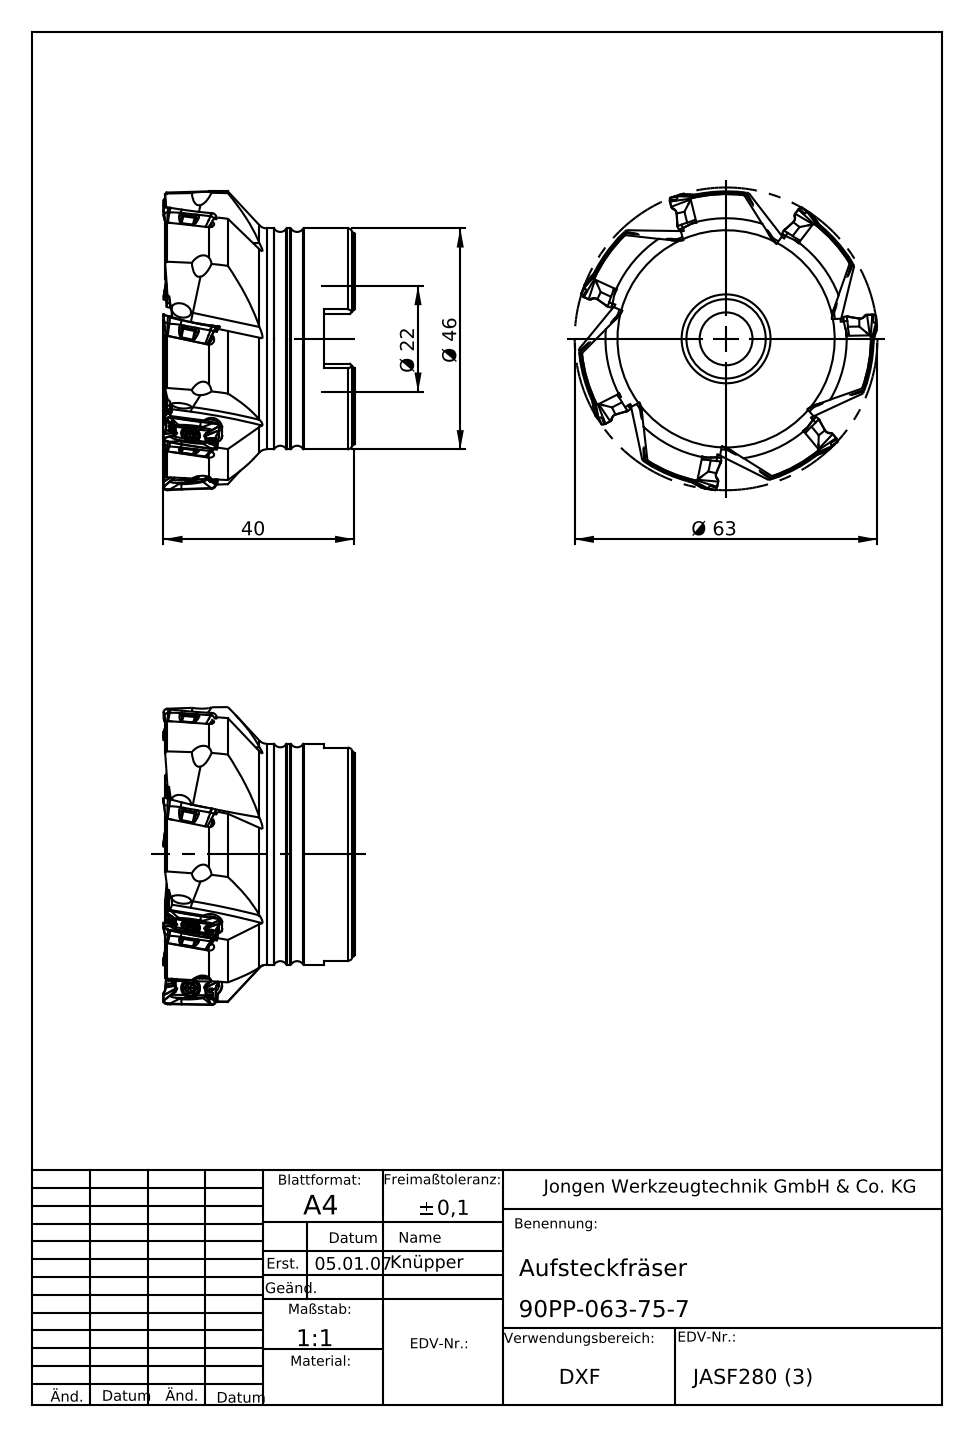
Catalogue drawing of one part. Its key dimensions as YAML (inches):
part_name: "90PP-063-75-7"
step_written_by: "SolidWorks 2012 (AUTOMOTIVE_DESIGN)"
units: inches
bodies: {solids: 1, faces: 296, planar: 102, cylindrical: 91, other: 103}
overall_size: [2.48, 2.48, 1.575]
volume: 4.104
surface_area: 27.48
round_holes:
  - {diameter: 0.118, count: 7}
  - {diameter: 0.433, count: 1}
  - {diameter: 0.65, count: 1}
  - {diameter: 0.866, count: 1}
  - {diameter: 0.872, count: 1}
  - {diameter: 0.878, count: 1}
  - {diameter: 2.074, count: 1}
round_bosses_or_shafts:
  - {diameter: 2.48, count: 1}
  - {diameter: 1.811, count: 1}
partial_cylinders:
  - {radius: 0.059, count: 14}
  - {radius: 0.083, count: 14}
  - {radius: 0.197, count: 7}
  - {radius: 0.988, count: 1}
  - {radius: 1.208, count: 1}
face_to_face_distances: [1.496, 0.248, 1.248, 0.906, 0.657, 0.591, 0.024, 1.102, 0.854, 0.197]
